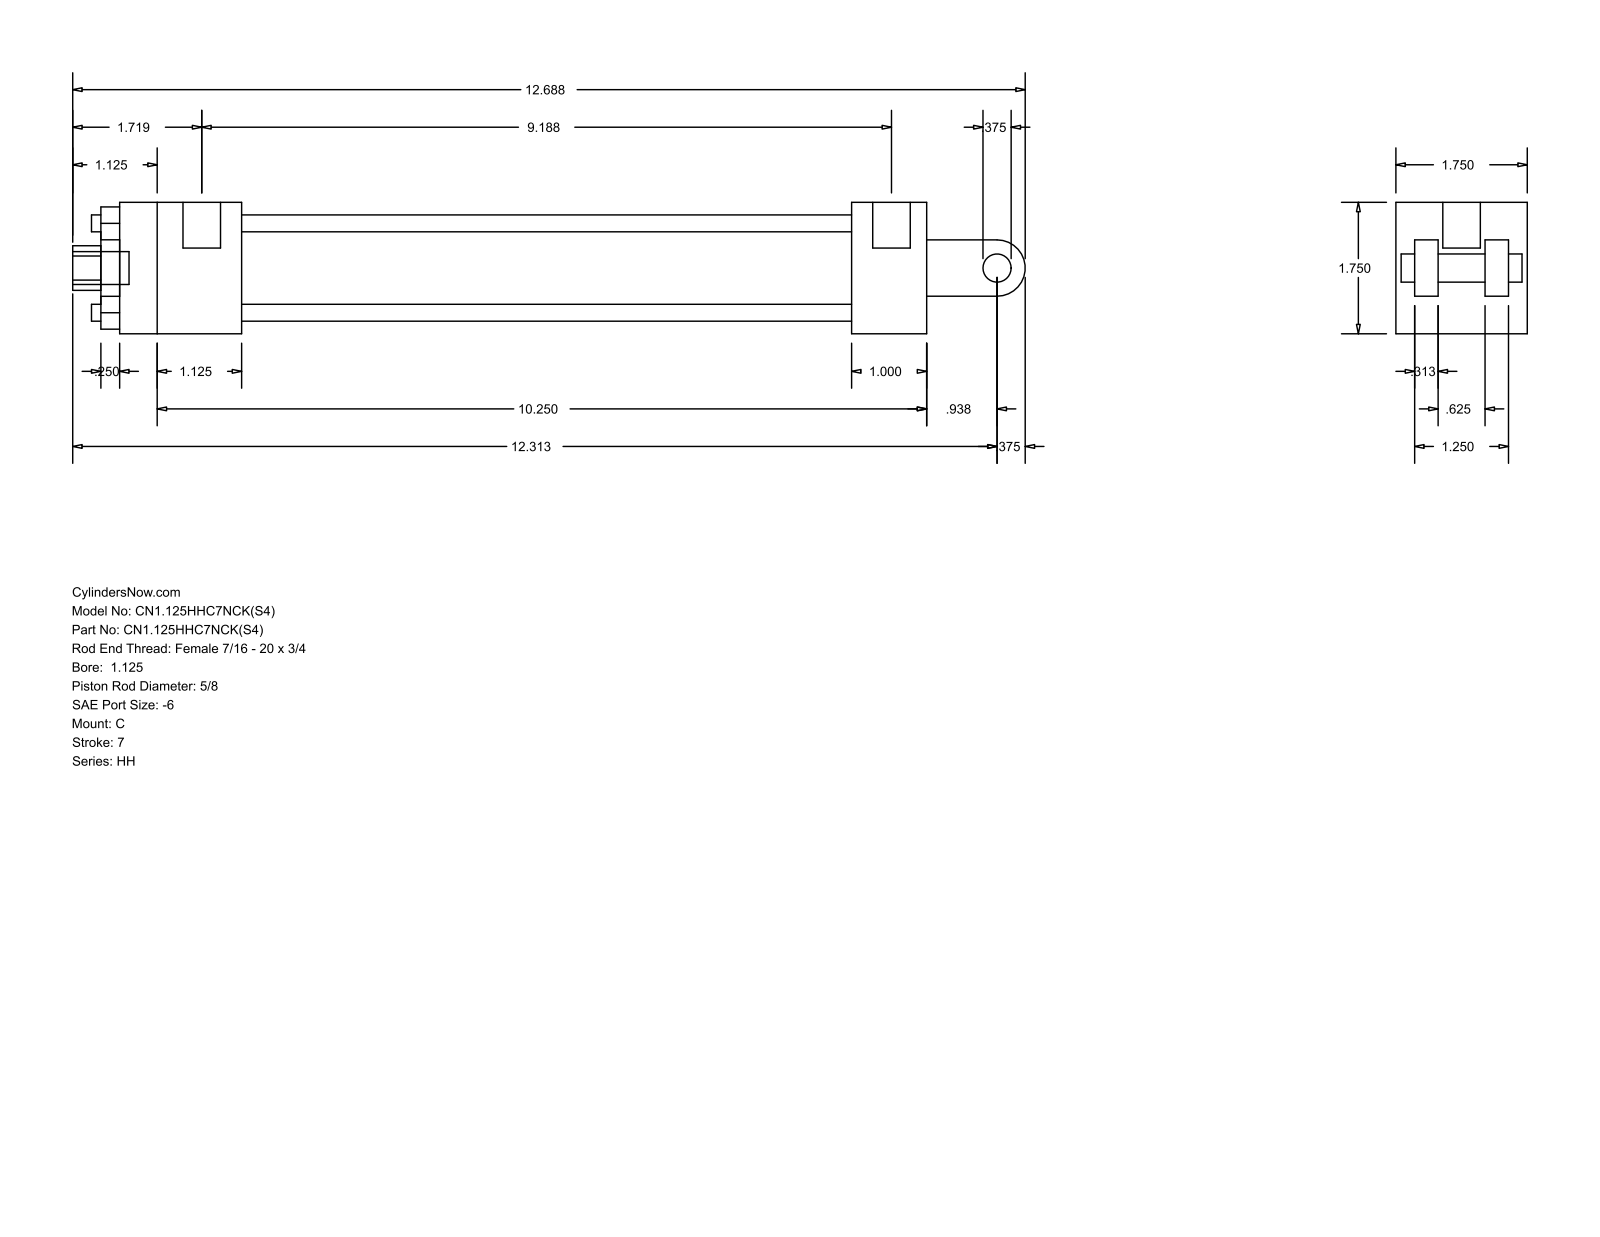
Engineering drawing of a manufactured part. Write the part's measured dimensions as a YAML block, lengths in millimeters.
part_name: "HH_C__0112_0.625"
step_written_by: "GSSL Pune (CONFIG_CONTROL_DESIGN)"
units: millimeters
bodies: {solids: 0, faces: 99, planar: 70, cylindrical: 29, other: 0}
overall_size: [322.26, 44.45, 44.45]
round_holes:
  - {diameter: 5.71, count: 4}
  - {diameter: 5.56, count: 2}
  - {diameter: 12.7, count: 1}
  - {diameter: 15.88, count: 1}
  - {diameter: 28.57, count: 1}
  - {diameter: 34.92, count: 1}
round_bosses_or_shafts:
  - {diameter: 5.56, count: 2}
  - {diameter: 12.7, count: 1}
  - {diameter: 11.11, count: 1}
  - {diameter: 9.53, count: 1}
partial_cylinders:
  - {radius: 7.54, count: 1}
  - {radius: 9.53, count: 1}
face_to_face_distances: [44.46, 6.35, 31.76, 14.29, 12.7, 30.17, 38.11, 7.94, 23.82, 41.27]
hole_center_spacings: [21.37, 30.22, 42.74]
